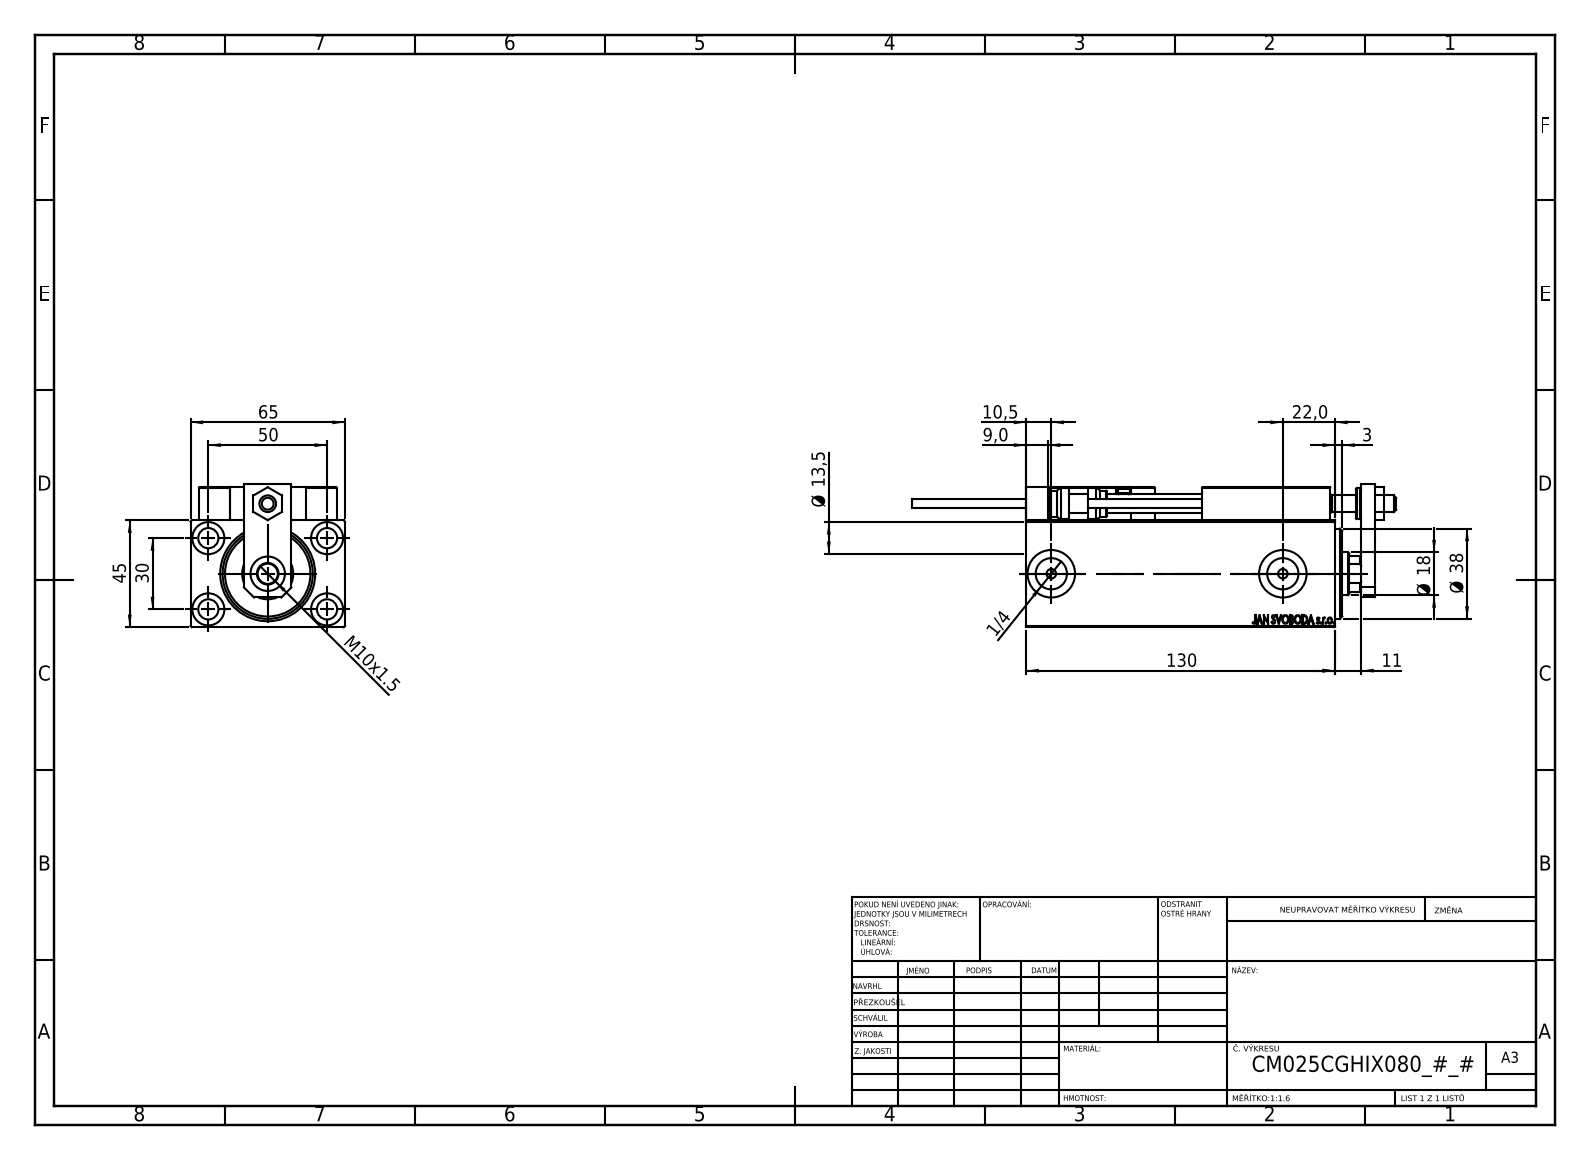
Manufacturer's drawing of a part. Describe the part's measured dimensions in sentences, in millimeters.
The part is named "SWITCH X; NUT_D12; SWITCH DIM B,W; ALLEN BOLT D5 (+7 more)". Its 3-D file was written by "SolidWorks 2019 (CONFIG_CONTROL_DESIGN)". It is 23 solids with 1282 faces: 560 planar, 188 cylindrical and 534 other. Overall it measures 203.7 by 65 by 60.5 millimeters. Its volume is 373 793 cubic millimeters and its surface area 98 342 square millimeters. Round holes: 6 of diameter 4, 5 of diameter 8, 5 of diameter 8.5, 4 of diameter 3.2, 4 of diameter 13.5, 2 of diameter 5, 2 of diameter 13.16, 2 of diameter 20, 1 of diameter 7, 1 of diameter 14.5, 1 of diameter 18, 1 of diameter 21.5. Round bosses or shafts: 2 of diameter 5, 2 of diameter 3.8, 1 of diameter 13, 1 of diameter 11. Partial cylindrical surfaces (rounded edges, fillets, slot ends): 30 of radius 0.3, 2 of radius 3, 1 of radius 8.5. The main face-to-face distances are 45, 65, 14, 6, 59, 3, 13, 3.5, 7, 20. The hole center spacings are 29.15, 11.37, 20, 28.9, 29.59, 29.69, 30, 36.06.
